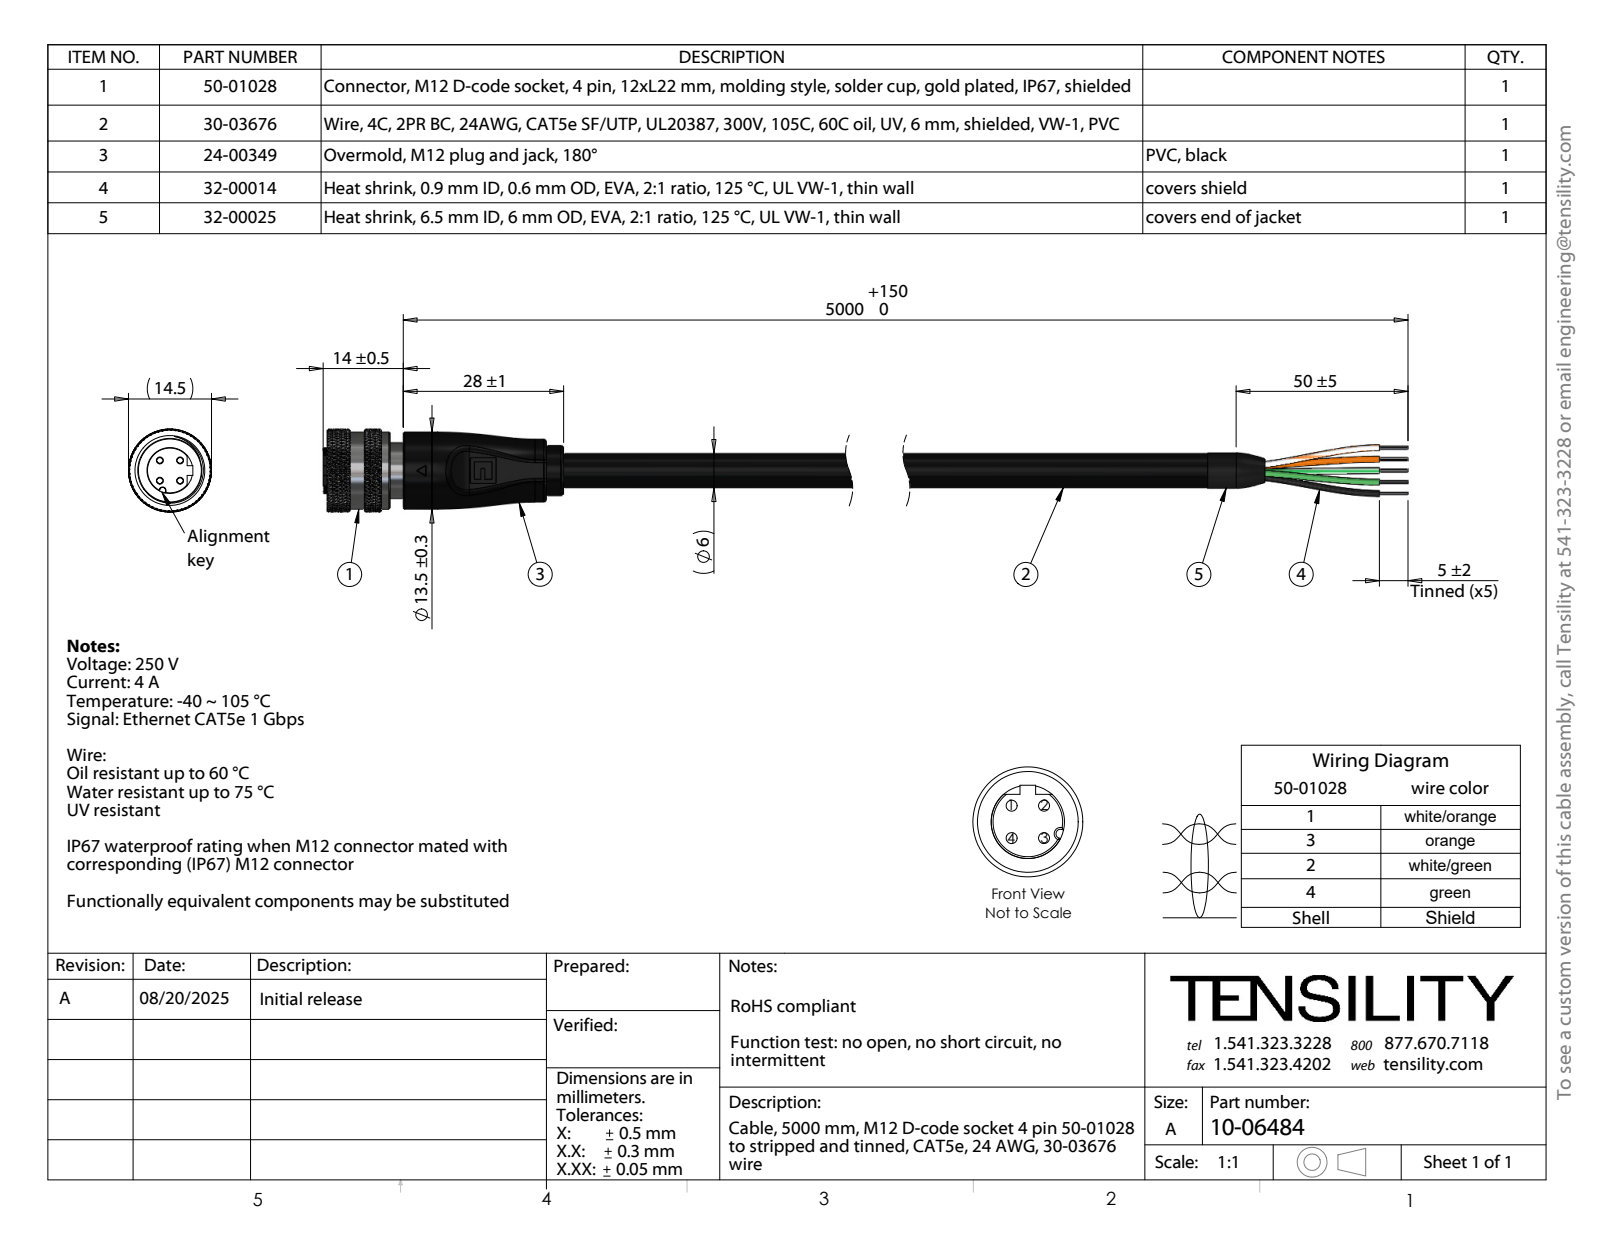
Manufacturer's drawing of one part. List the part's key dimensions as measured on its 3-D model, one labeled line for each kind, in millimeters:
Part name (STEP PRODUCT): 50-01028-04_默认; 50-01028-02_默认; 50-01028-05_默认; 30-03676_s + t (+5 more)
STEP written by: SolidWorks 2025 (CONFIG_CONTROL_DESIGN)
Units: millimetres
Bodies: 87 solids, 3550 faces (339 planar, 940 cylindrical, 2271 other)
Overall size (bounding box): 222 × 14.5 × 14.5
Volume: 9 616 mm³ · Surface area: 27 027 mm²
Round holes (diameter × count): ⌀0.2 ×28, ⌀1.05 ×4, ⌀1.1 ×4, ⌀1.2 ×4, ⌀3.16 ×1, ⌀3.21 ×1, ⌀3.36 ×1, ⌀9 ×1, ⌀10 ×1, ⌀11.2 ×1
Round bosses / shafts (diameter × count): ⌀0.2 ×35, ⌀1.6 ×4, ⌀1.5 ×4, ⌀13.5 ×1, ⌀11 ×1, ⌀10.6 ×1, ⌀10.5 ×1, ⌀9.8 ×1
Partial cylindrical surfaces — rounded edges, fillets, slot ends (radius × count): R0.1 ×10, R0.4 ×6, R0.5 ×2, R1.5 ×2, R4 ×1, R5 ×1, R5.58 ×1, R6.75 ×1
Main face-to-face distances: 178, 28, 150, 7, 4.7, 1, 31.8, 3.5, 23.3, 173.3
Hole centre spacings: 1.91, 0.36, 2.09, 1.06, 0.89, 1.08, 1.24, 1.8
